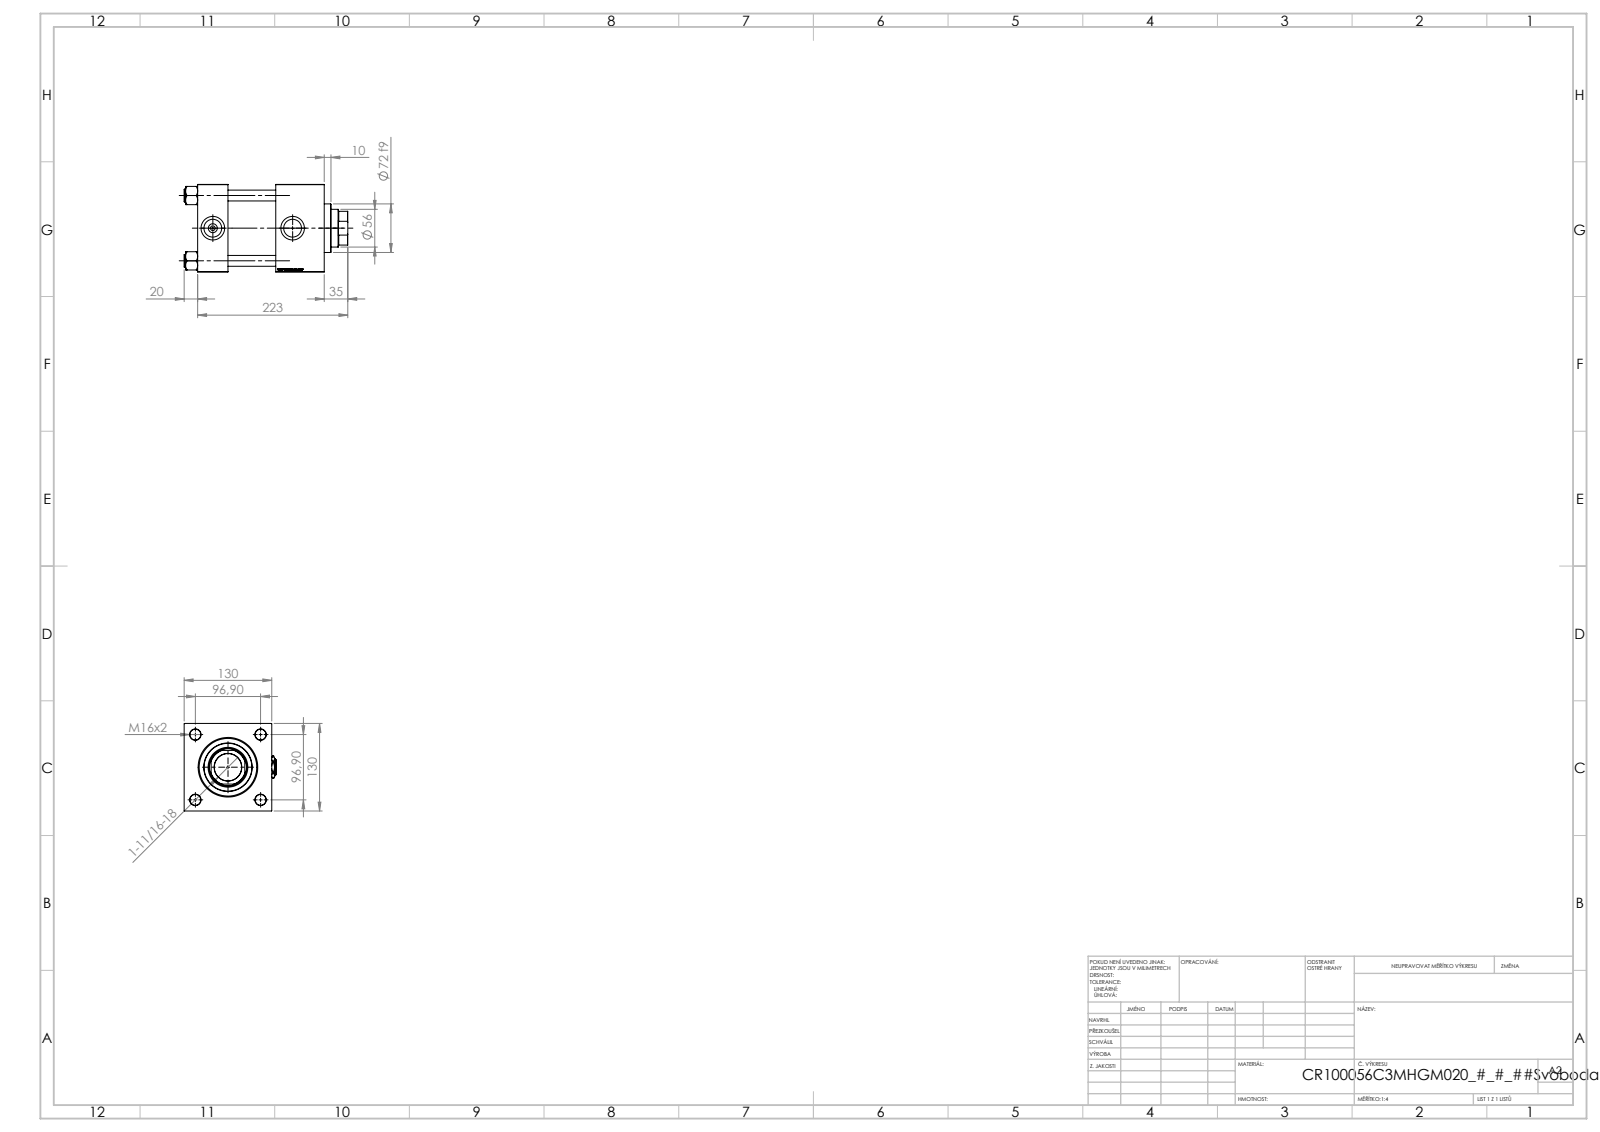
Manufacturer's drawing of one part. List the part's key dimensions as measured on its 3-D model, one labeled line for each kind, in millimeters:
Part name (STEP PRODUCT): Zatka_pro_OIL_PORT; V215_VC_A; V215CR_C_Body; V215CR_VCP_C (+2 more)
STEP written by: SolidWorks 2019 (CONFIG_CONTROL_DESIGN)
Units: millimetres
Bodies: 13 solids, 1297 faces (621 planar, 98 cylindrical, 578 other)
Overall size (bounding box): 243 × 137 × 130
Volume: 2 461 000 mm³ · Surface area: 340 431 mm²
Round holes (diameter × count): ⌀16 ×4, ⌀7 ×2, ⌀26.44 ×2, ⌀35 ×2, ⌀40.5 ×1, ⌀56 ×1, ⌀59 ×1, ⌀76 ×1, ⌀85.5 ×1, ⌀100 ×1
Round bosses / shafts (diameter × count): ⌀19 ×4, ⌀106 ×1, ⌀72 ×1
Partial cylindrical surfaces — rounded edges, fillets, slot ends (radius × count): R27 ×1
Main face-to-face distances: 130, 45, 188, 143, 116, 71, 72, 20, 51, 92
Hole centre spacings: 68.52, 96.9, 137.04, 118.5
